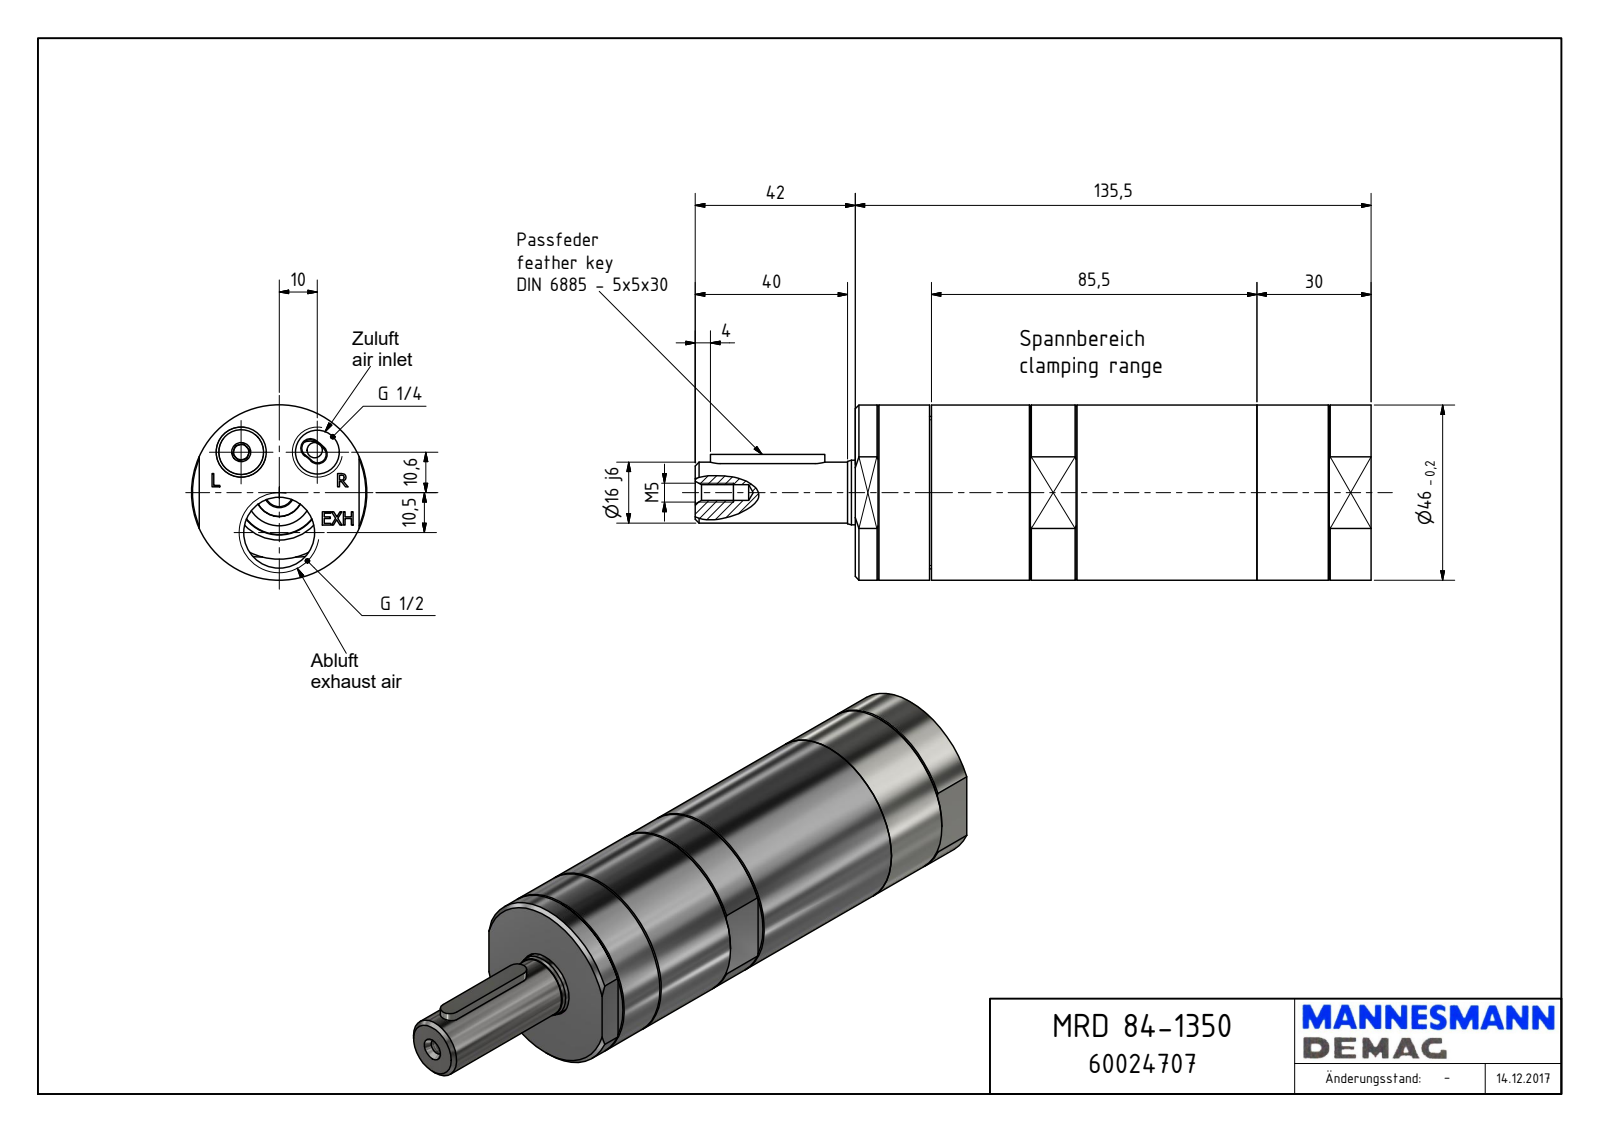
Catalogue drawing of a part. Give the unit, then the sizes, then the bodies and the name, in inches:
Units: inches
Overall size (bounding box): 6.988 × 1.811 × 1.811
Round holes (diameter × count): ⌀0.157 ×1, ⌀0.163 ×1, ⌀0.451 ×1, ⌀0.689 ×1, ⌀0.733 ×1
Round bosses / shafts (diameter × count): ⌀1.811 ×1, ⌀1.575 ×1, ⌀1.329 ×1, ⌀0.667 ×1, ⌀0.63 ×1
Partial cylindrical surfaces — rounded edges, fillets, slot ends (radius × count): R0.098 ×2, R0.197 ×2, R0.225 ×1, R0.748 ×1
Main face-to-face distances: 5.335, 1.654, 0.768, 0.787, 0.02, 4.567, 4.547, 5.045, 4.277, 4.257
Hole centre spacings: 0.574, 0.919, 0.413, 0.787
Volume: 13.92 in³ · Surface area: 43.75 in²
Bodies: 1 solid, 164 faces (105 planar, 28 cylindrical, 31 other)
Part name (STEP PRODUCT): MRD 84-1350_60024707
STEP written by: Autodesk Inventor 2018 (AUTOMOTIVE_DESIGN)
